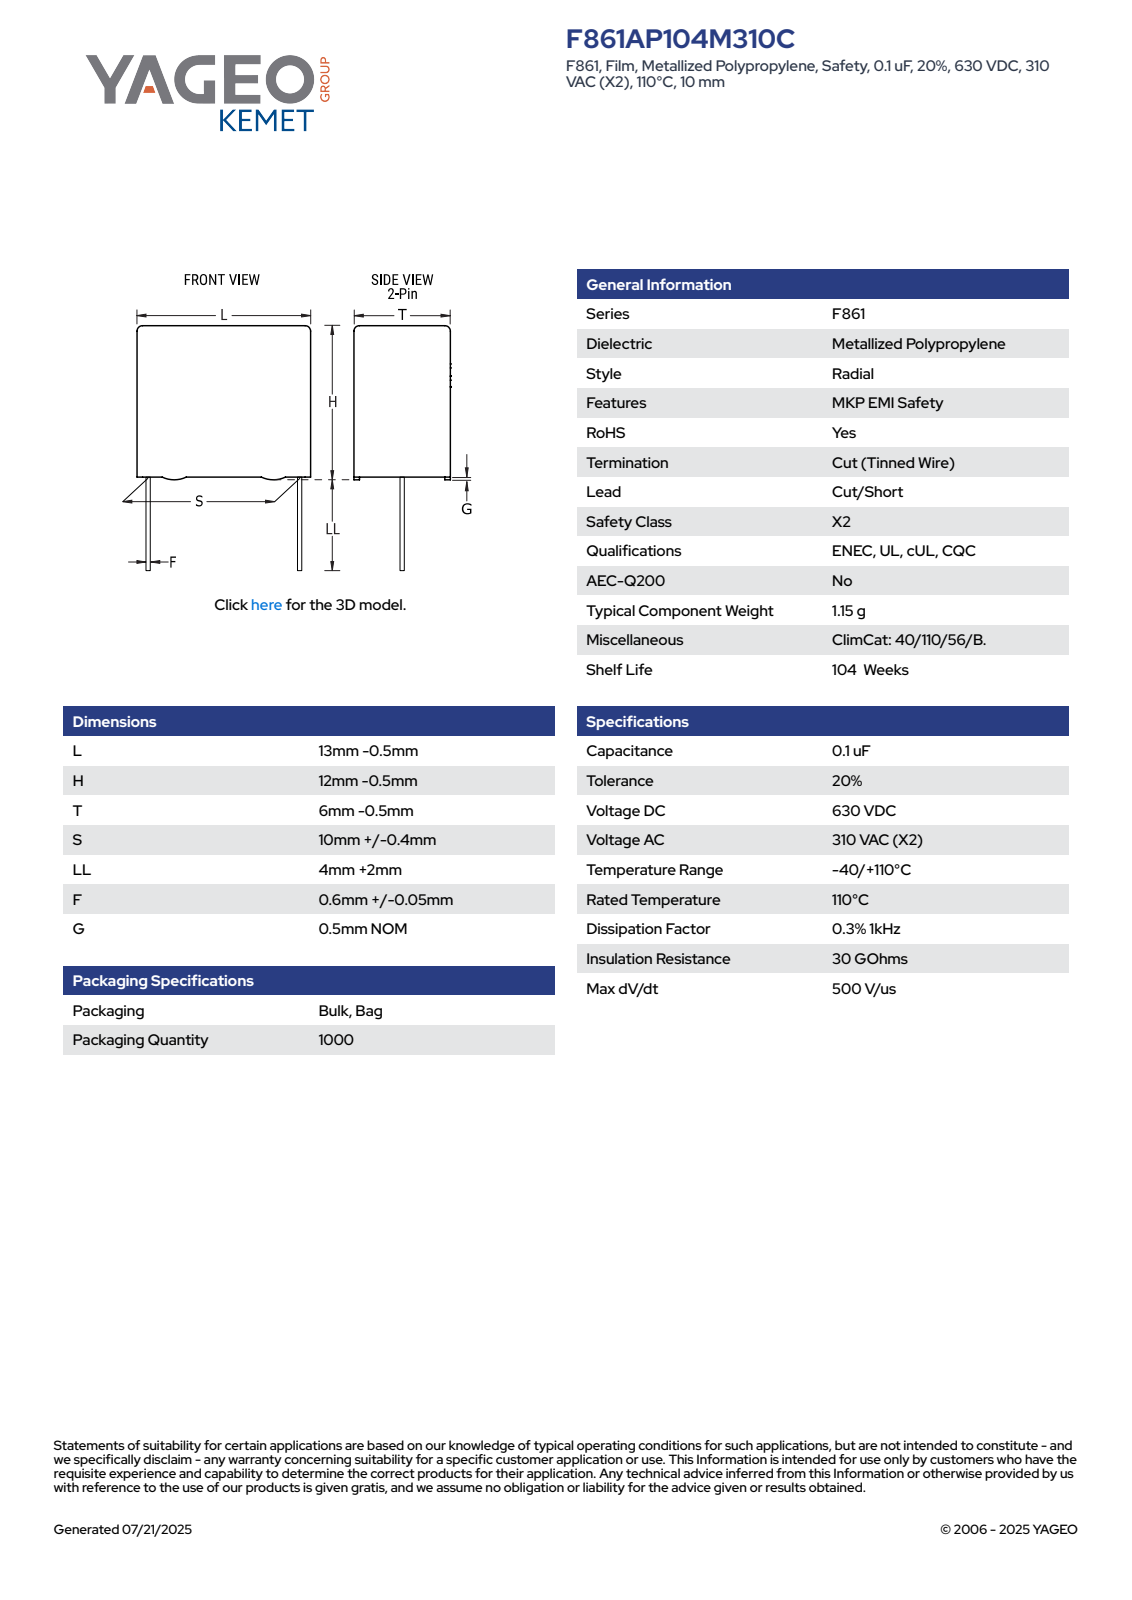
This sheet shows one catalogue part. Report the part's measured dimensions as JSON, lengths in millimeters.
{"part_name": "CFR_RBG_13X12X6_L12.5H11.5T5.5S10LL6F0.65G0.5", "step_written_by": "SolidWorks 2014 (AUTOMOTIVE_DESIGN)", "units": "millimeters", "bodies": {"solids": 4, "faces": 89, "planar": 81, "cylindrical": 8, "other": 0}, "overall_size": [17.5, 12.5, 5.5], "volume_mm3": 760, "surface_area_mm2": 578, "round_bosses_or_shafts": [[0.65, 2]], "partial_cylinders_radius": [[0.5, 4]], "face_to_face_distances": [5.5, 12.5, 11, 0.31, 5.19, 0.5, 11.5, 4.88, 6, 6.5]}
